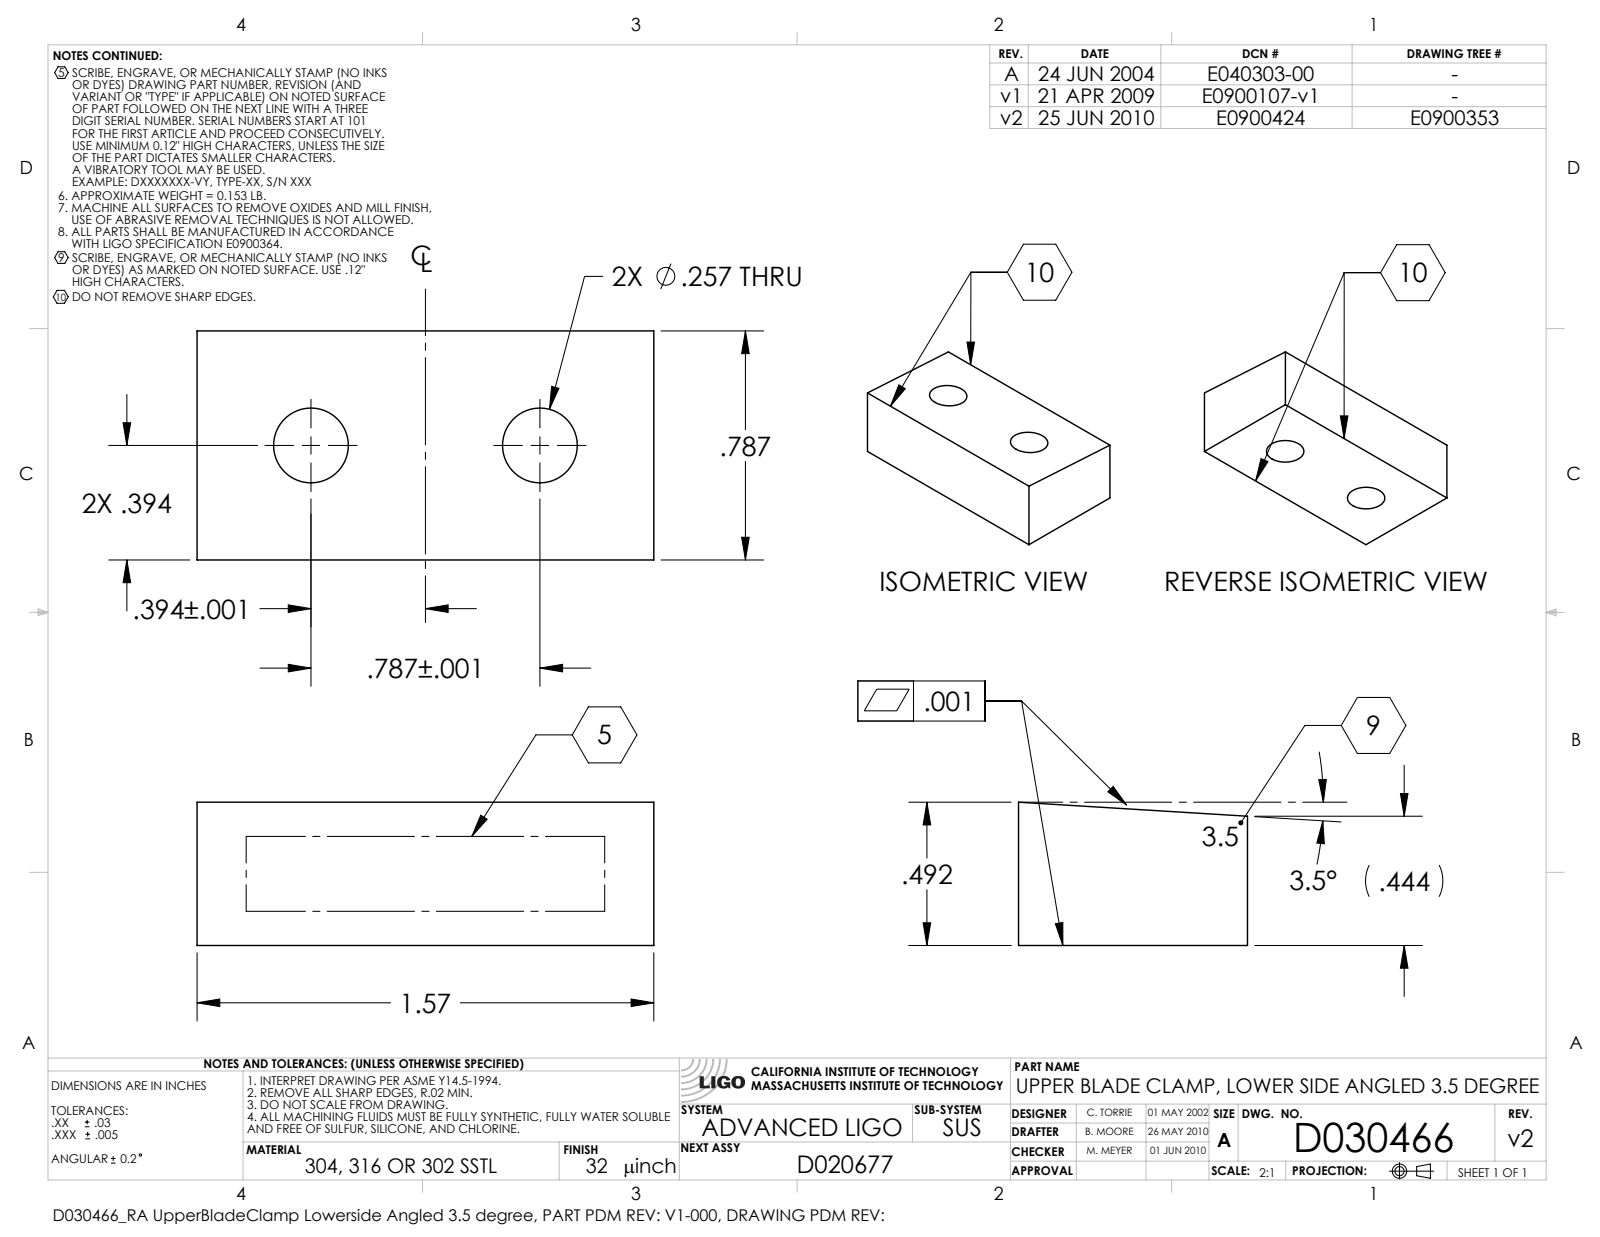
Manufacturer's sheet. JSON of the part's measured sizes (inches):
{"part_name": "D030466-v2_aLIGO_SUS_HSTS_Upper Blade Clamp, Lower Side, Angled 3.5", "step_written_by": "SolidWorks 2009 (CONFIG_CONTROL_DESIGN)", "units": "inches", "bodies": {"solids": 1, "faces": 10, "planar": 6, "cylindrical": 4, "other": 0}, "overall_size": [1.57, 0.787, 0.492], "volume_in3": 0.53, "surface_area_in2": 5.229, "round_holes": [[0.257, 2]], "face_to_face_distances": [0.787, 1.57], "hole_center_spacings": [0.787]}
